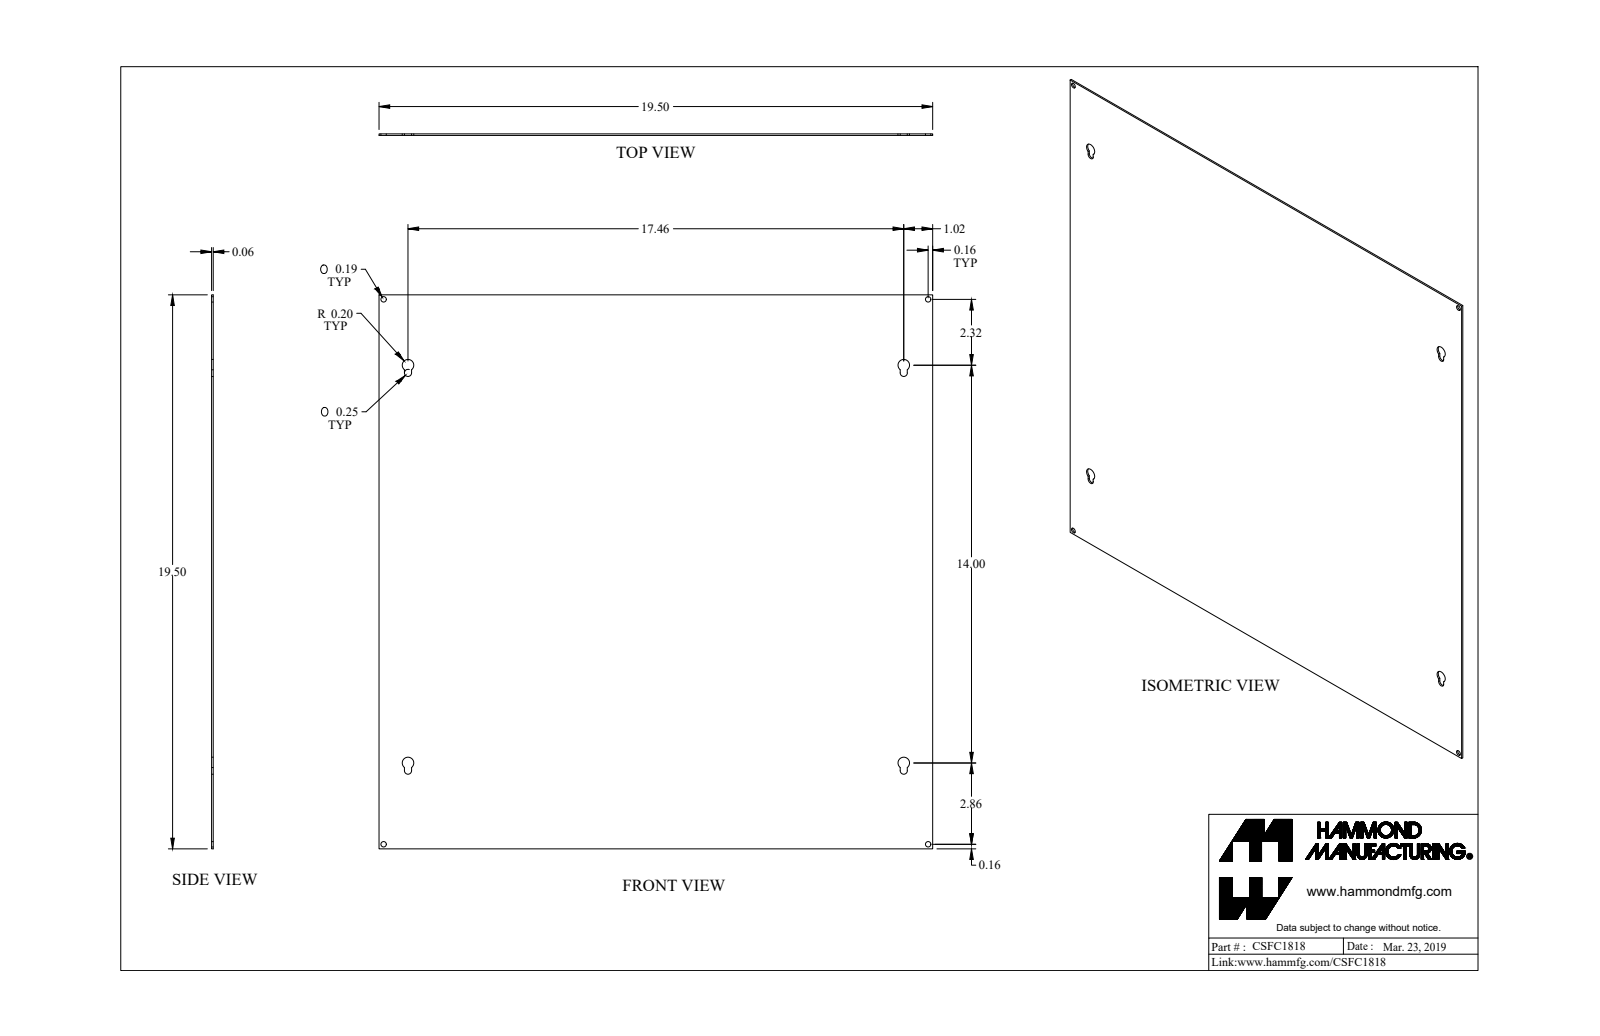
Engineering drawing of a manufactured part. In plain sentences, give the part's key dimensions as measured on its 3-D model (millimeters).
The part is named "CSFC1818_Default". Its 3-D file was written by "SolidWorks 2019 (CONFIG_CONTROL_DESIGN)". It is 1 solid with 38 faces: 14 planar, 24 cylindrical and 0 other. Overall it measures 495.3 by 495.3 by 1.4 millimeters. Its volume is 354 500 cubic millimeters and its surface area 492 800 square millimeters. Round holes: 4 of diameter 4.8. Partial cylindrical surfaces (rounded edges, fillets, slot ends): 4 of radius 3.2, 4 of radius 5.2. The main face-to-face distances are 1.4, 495.3, 22.7, 472.6, 29.1, 466.2, 6.4, 443.5, 449.8, 437.1. The hole center spacings are 487.2, 689.
